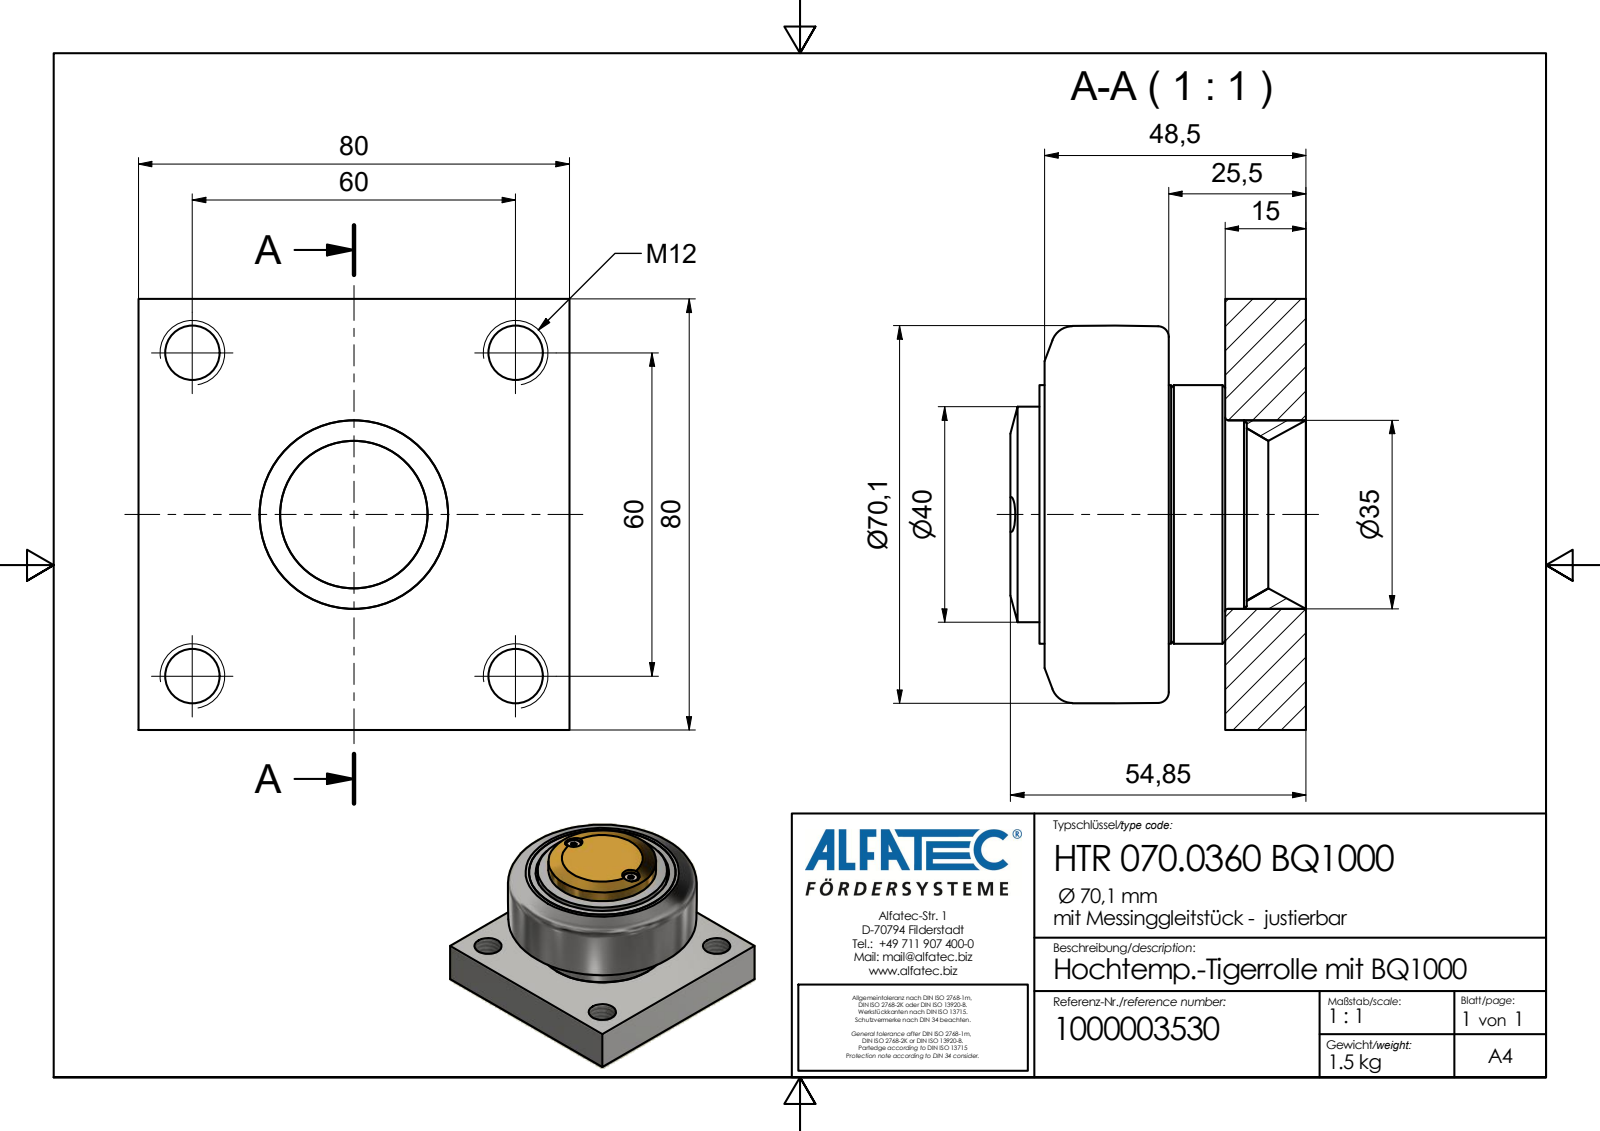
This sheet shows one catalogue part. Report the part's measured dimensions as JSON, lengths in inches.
{"part_name": "HTR 070.0360 BQ1000_Kontur", "step_written_by": "Autodesk Inventor 2020 (AP242_MANAGED_MODEL_BASED_3D_ENGINEERING_MIM_LF)", "units": "inches", "bodies": {"solids": 1, "faces": 50, "planar": 28, "cylindrical": 12, "other": 10}, "overall_size": [3.15, 3.15, 2.159], "volume_in3": 12.17, "surface_area_in2": 46.75, "round_holes": [[0.398, 4], [0.256, 2]], "round_bosses_or_shafts": [[0.211, 2], [1.89, 1], [1.575, 1]], "face_to_face_distances": [0.591, 3.15, 1.004, 0.413, 1.909, 1.319, 0.906, 2.159, 1.569, 1.156], "hole_center_spacings": [1.32, 2.129, 2.362, 3.341, 1.181]}
